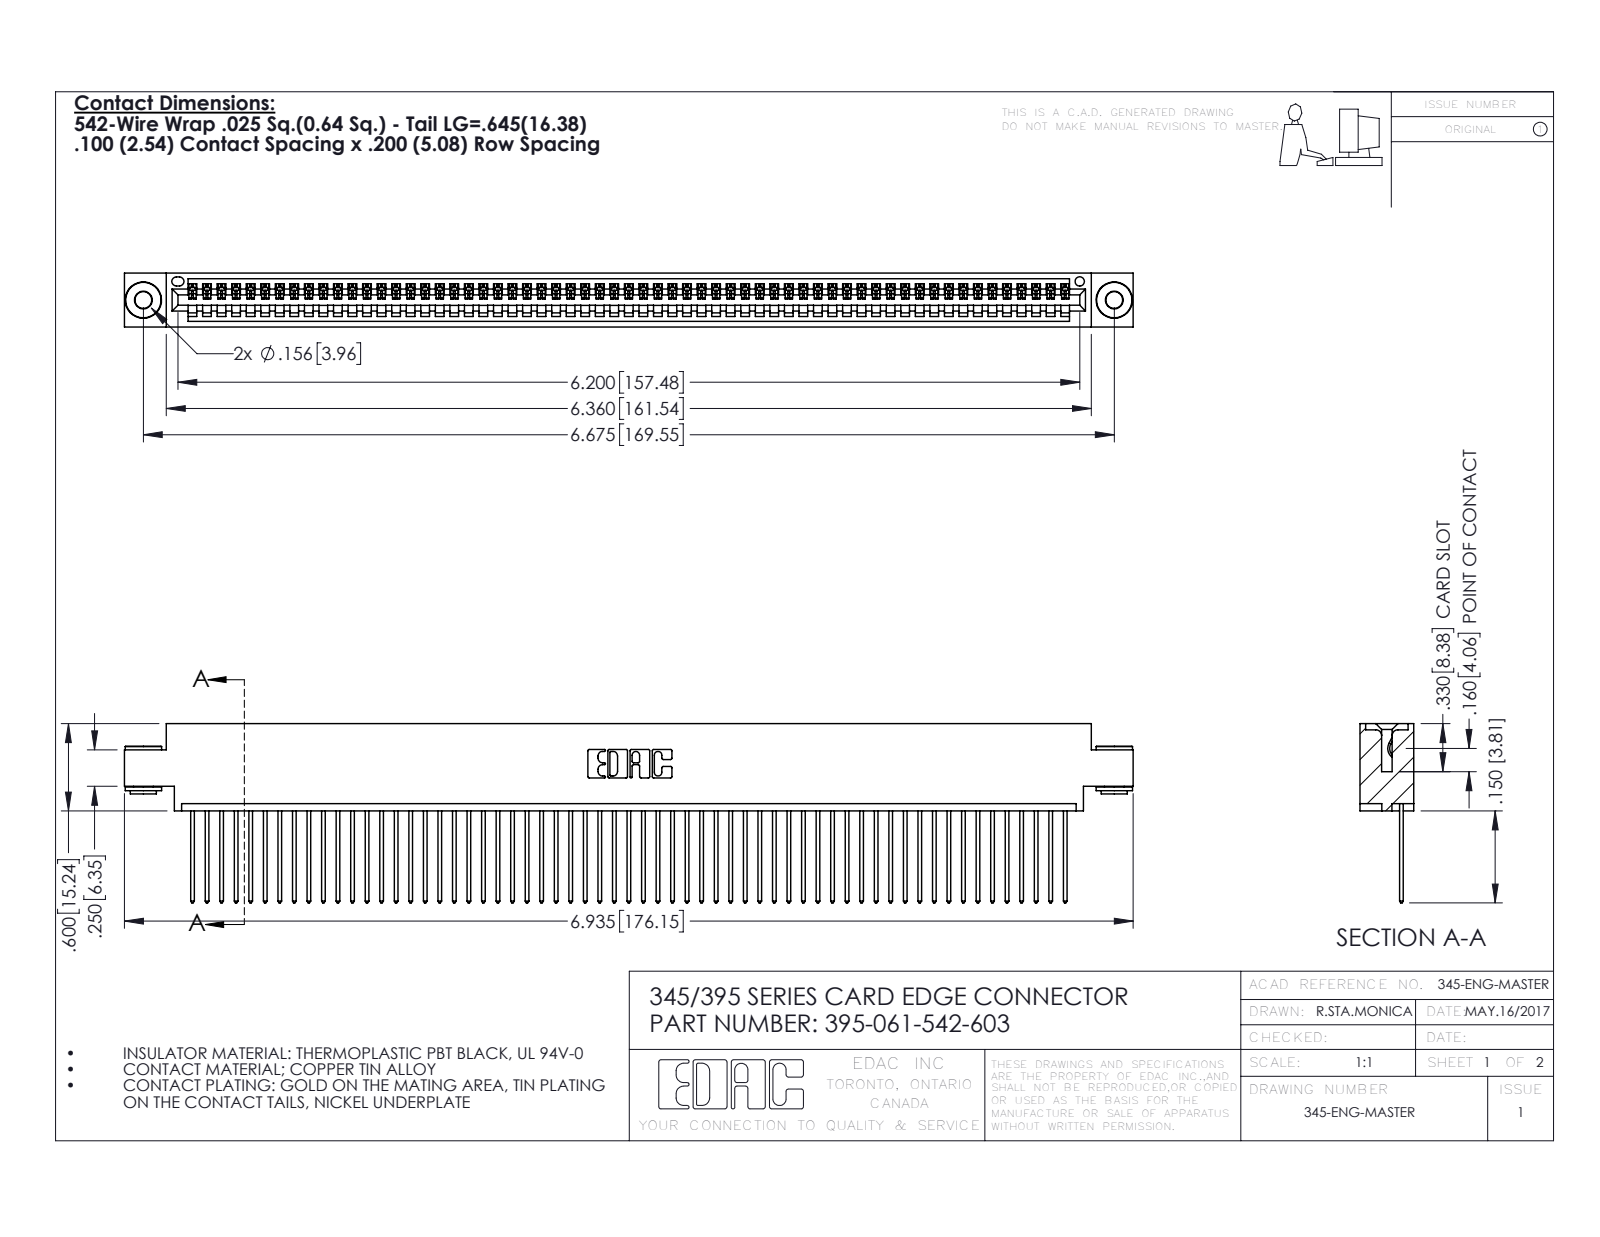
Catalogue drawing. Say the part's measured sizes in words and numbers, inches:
The part is named "345 Part_0.170 Offset - 0.156 Dia-TH; 345-292-001_345-293-142; 395-061-542-603; 345-250-002_345-250-002-102". Its 3-D file was written by "SolidWorks 2016 (CONFIG_CONTROL_DESIGN)". It is 64 solids with 3706 faces: 2534 planar, 1164 cylindrical and 8 other. Overall it measures 6.935 by 1.232 by 0.37 inches. Its volume is 1.033 cubic inches and its surface area 37.13 square inches. Round holes: 2 of diameter 0.116, 2 of diameter 0.156, 1 of diameter 0.064. Round bosses or shafts: 2 of diameter 0.25, 2 of diameter 0.18, 2 of diameter 0.136. Partial cylindrical surfaces (rounded edges, fillets, slot ends): 122 of radius 0.006, 122 of radius 0.01, 22 of radius 0.01, 6 of radius 0.007, 6 of radius 0.031, 3 of radius 0.026, 2 of radius 0.031, 2 of radius 0.04. The main face-to-face distances are 0.072, 0.298, 0.37, 0.098, 0.272, 0.025, 0.2, 0.225, 0.175, 0.149. The hole center spacings are 0.27, 6.439, 6.675.
